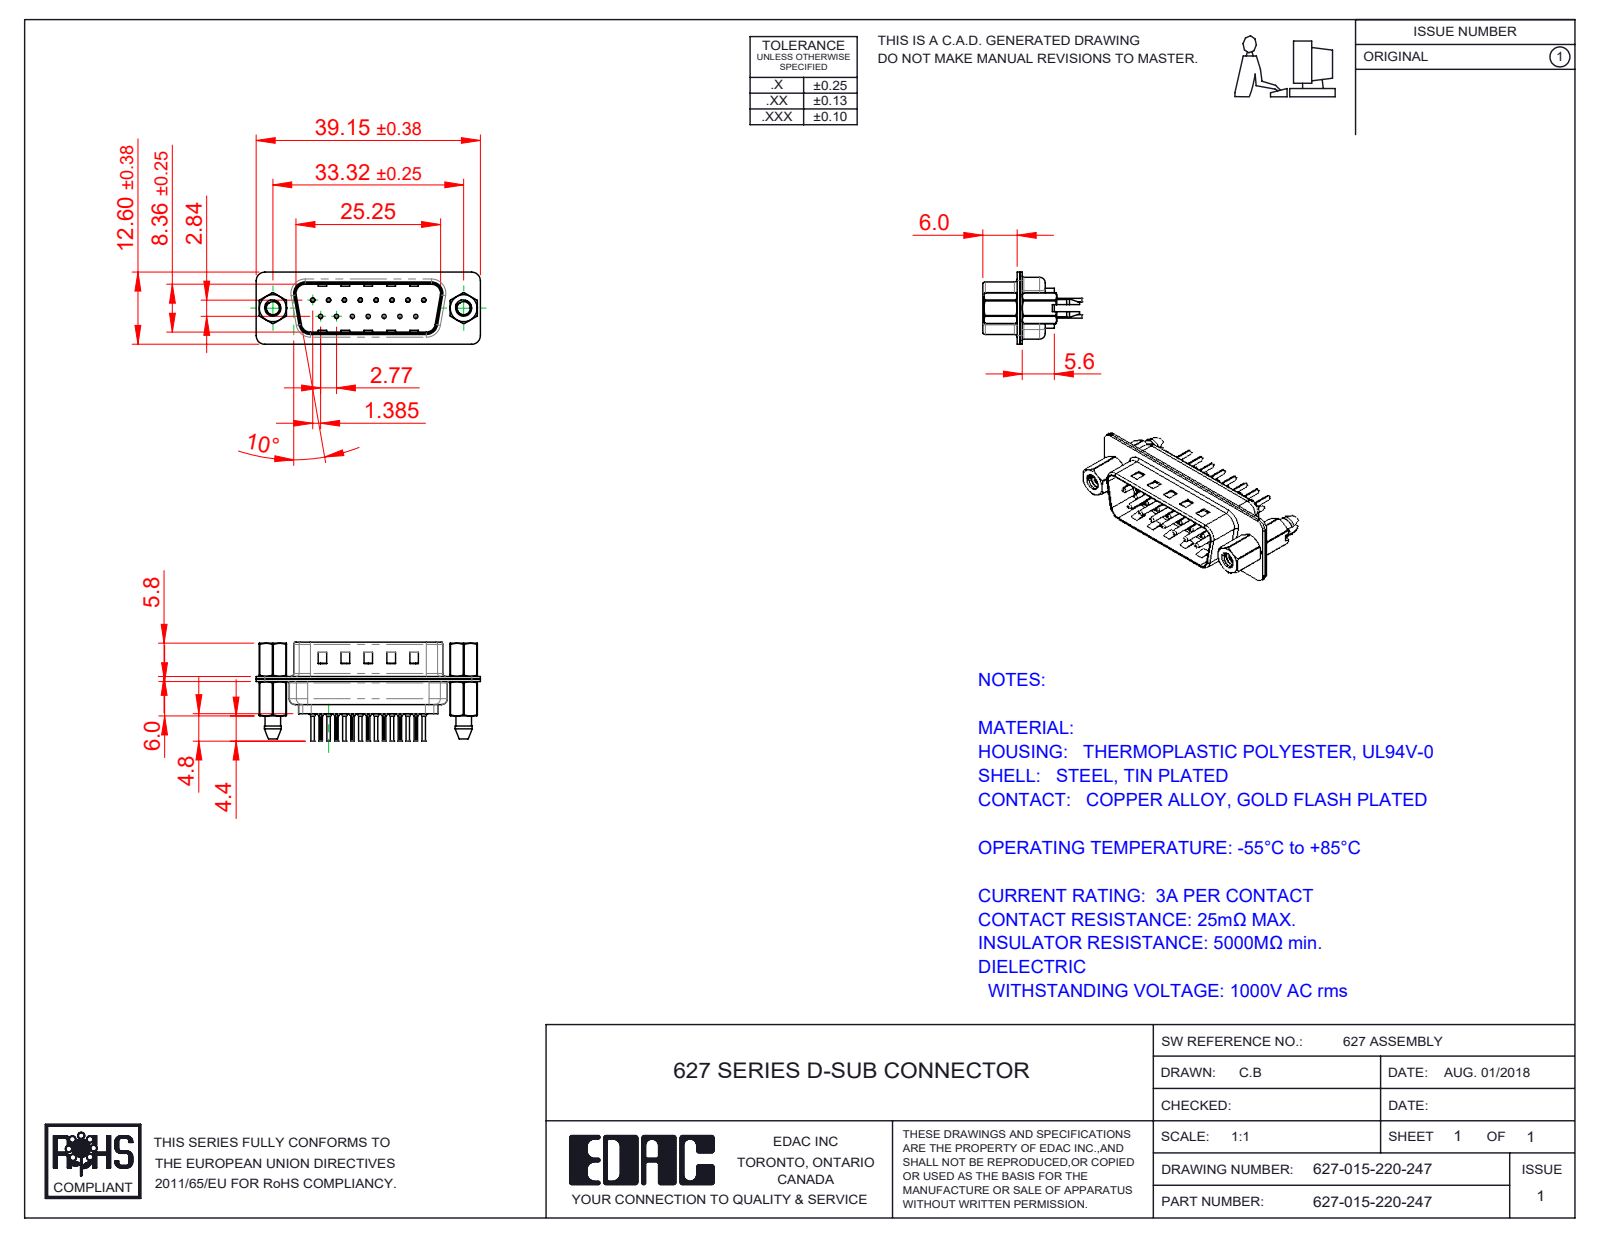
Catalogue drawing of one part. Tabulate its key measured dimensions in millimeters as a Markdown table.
| quantity | value |
| --- | --- |
| part name | 627 4-40 Threaded Boardlock_LP; 627 Contact Row 1_20L; 627 Shell Front_15 Contacts; 627 Housing_15 LP (+4 more) |
| STEP written by | SolidWorks 2020 (CONFIG_CONTROL_DESIGN) |
| units | millimeters |
| bodies | 22 solids, 2010 faces (553 planar, 792 cylindrical, 665 other) |
| overall size | 39.15 × 17.3 × 12.6 |
| volume | 2 158 mm³ |
| surface area | 6 166 mm² |
| round holes (diameter × count) | 0.2 × 15, 0.35 × 15, 1.1 × 15, 1.6 × 15, 2.26 × 2, 2.29 × 2, 4 × 2, 4.8 × 2 |
| round bosses / shafts (diameter × count) | 2 × 15, 1.5 × 15, 0.75 × 15, 0.6 × 15, 4.9 × 2, 2.79 × 2 |
| partial cylindrical surfaces (radius × count) | 0.1 × 30, 1.5 × 18, 2 × 12, 1.6 × 10, 0.5 × 8, 0.25 × 4, 0.6 × 4, 0.65 × 4 |
| main face-to-face distances | 0.4, 0.45, 0.9, 0.82, 9.58, 8.76, 4.76, 1.5, 1.4, 6.5 |
| hole center spacings | 3.16, 2.77, 5.54, 8.31, 11.08, 5.03, 5.04, 7.48 |
